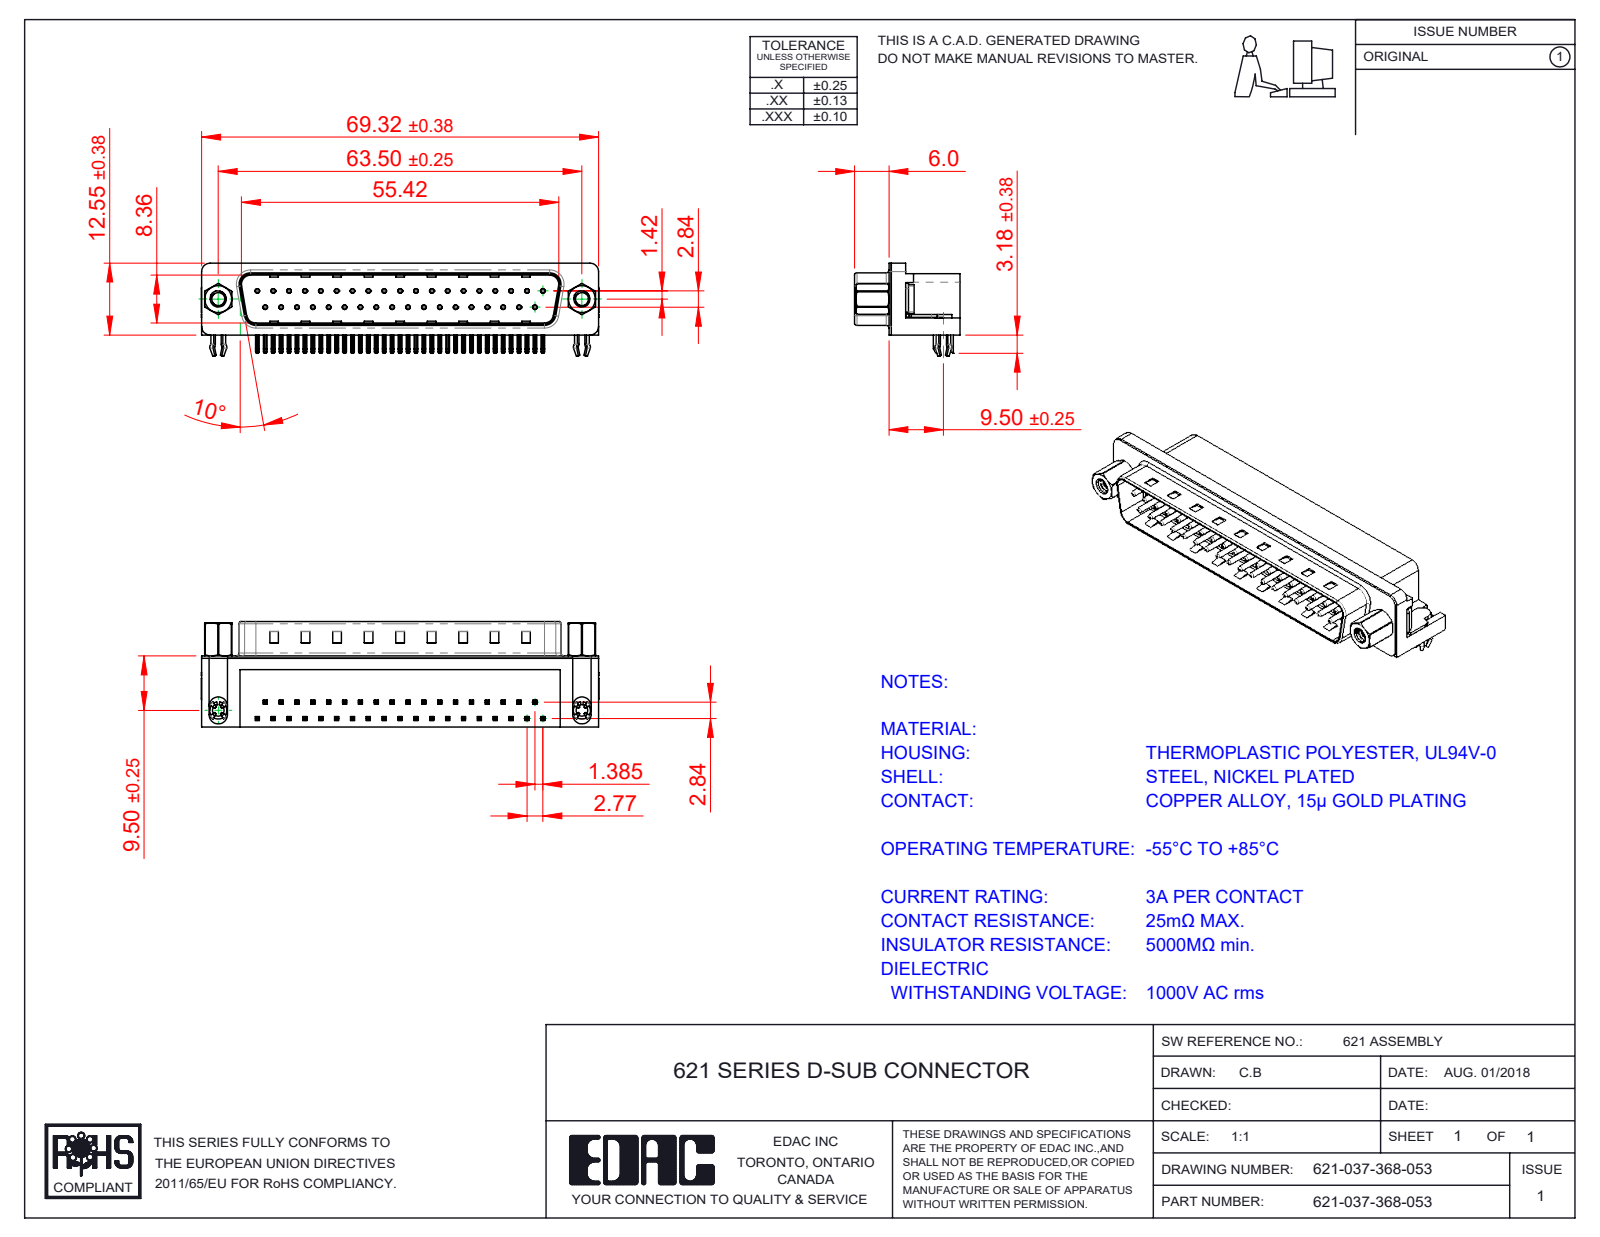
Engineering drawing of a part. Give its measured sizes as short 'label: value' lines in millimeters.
name: 621 Shell_37 Socket; 621 Contact Bottom; 621-037-368-053; 621 Housing_37 Socket (+4 more)
written by: SolidWorks 2016 (CONFIG_CONTROL_DESIGN)
unit: mm
bodies: 45 solids, 3355 faces (2035 planar, 999 cylindrical, 321 other)
size: 69.4 × 18.4 × 15.73
volume: 8 846 mm³; area: 10 656 mm²
holes: 37× ⌀0.35, 37× ⌀0.8, 4× ⌀2.26, 2× ⌀2.29, 2× ⌀4, 2× ⌀4.8, 2× ⌀5
bosses: 37× ⌀0.75, 2× ⌀4.9, 2× ⌀4.75, 2× ⌀3.9, 2× ⌀3.26, 2× ⌀2.79
rounds: 156× R0.25, 74× R0.12, 16× R1, 9× R0.5, 8× R1.6, 7× R1.5, 4× R0.9, 4× R2
face distances: 0.4, 12, 10.35, 8.76, 2.1, 1.7, 10.46, 10.86, 12.4, 9
hole spacings: 3.16, 2.77, 5.54, 8.31, 11.08, 13.85, 19.39, 22.16
